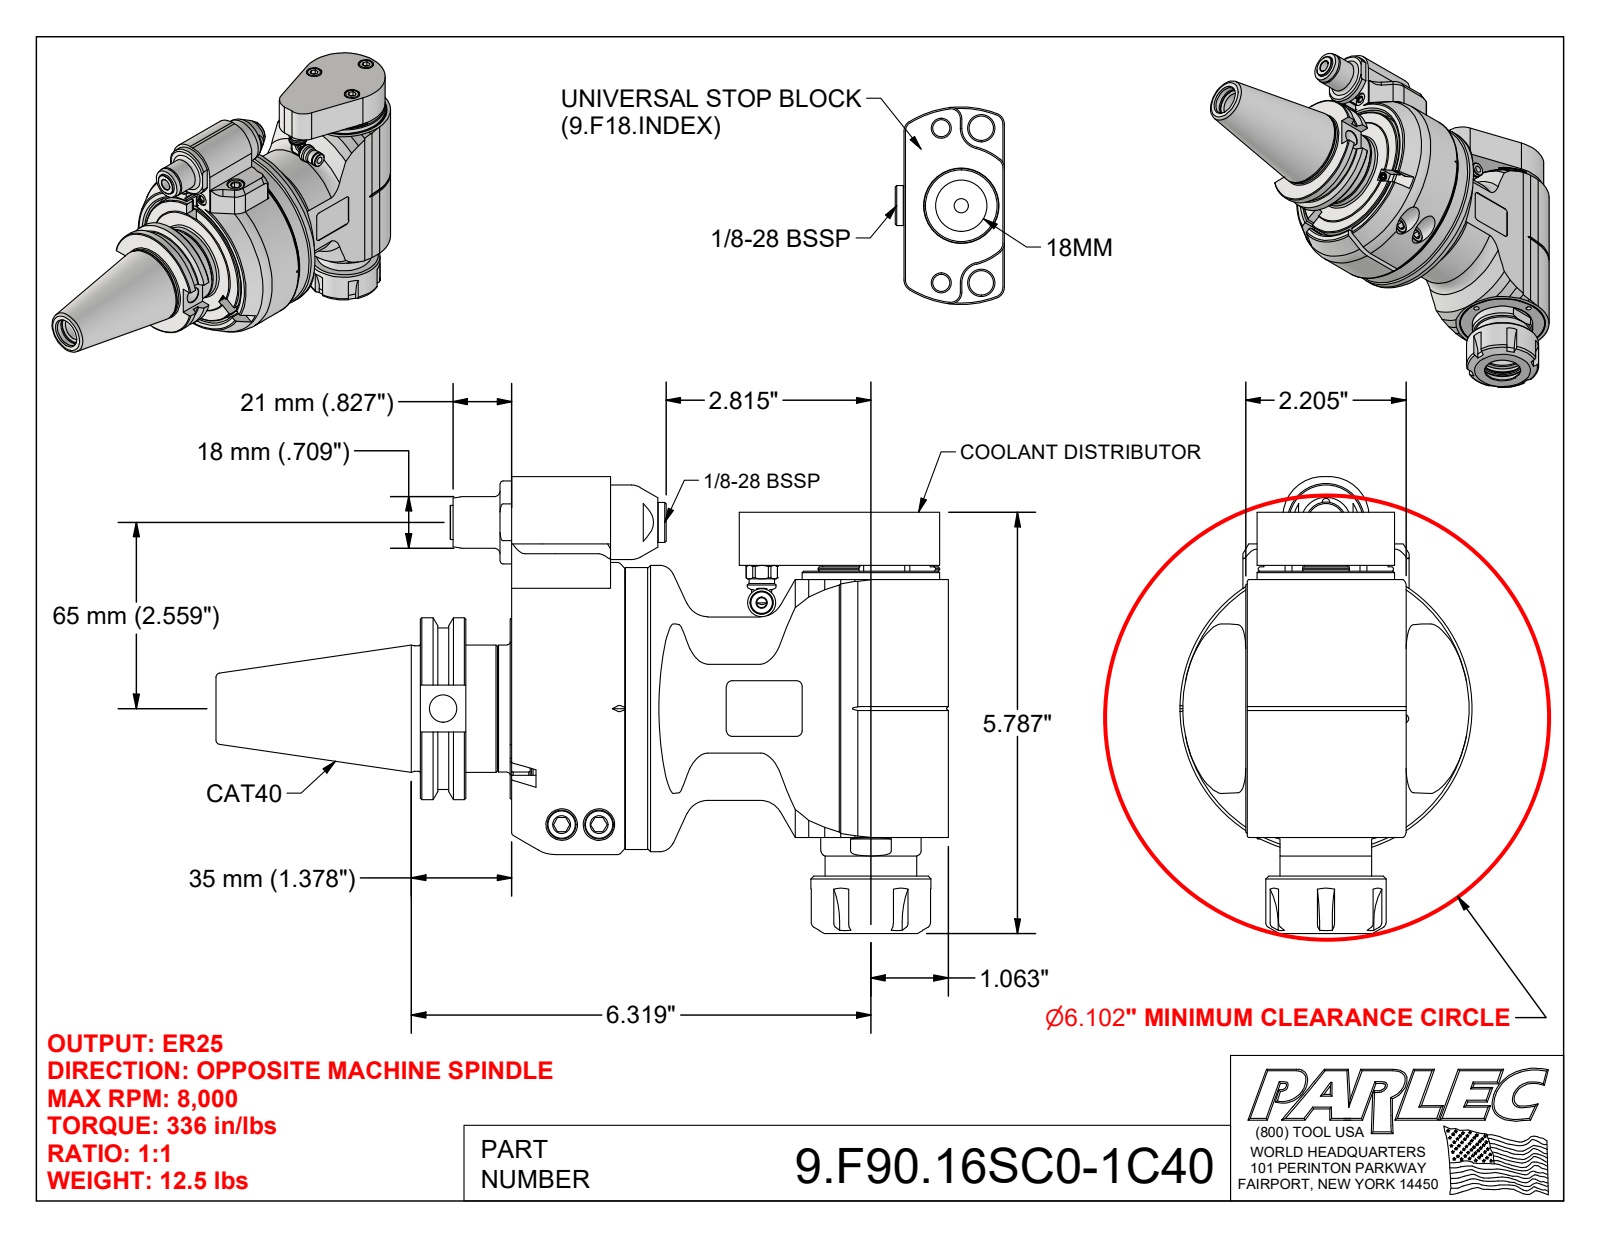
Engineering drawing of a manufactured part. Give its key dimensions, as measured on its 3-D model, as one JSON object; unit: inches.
{"part_name": "9.F90.16SC0-1C40; 9_F90_16SC0; 9_GA1_446_2 (EVO, Type 1, C40, 65mm, 35mm)", "step_written_by": "Autodesk Inventor 2022 (AUTOMOTIVE_DESIGN)", "units": "inches", "bodies": {"solids": 6, "faces": 887, "planar": 379, "cylindrical": 237, "other": 271}, "overall_size": [10.069, 6.28, 4.016], "volume_in3": 62.83, "surface_area_in2": 259.4, "round_holes": [[0.335, 21], [0.126, 8], [0.197, 3], [0.256, 3], [0.354, 3], [0.102, 2], [0.13, 2], [0.138, 2], [0.165, 2], [0.315, 2], [0.409, 2], [0.433, 2]], "round_bosses_or_shafts": [[0.394, 5], [0.335, 3], [0.709, 2], [0.472, 2], [0.315, 2], [0.236, 2], [0.098, 2], [4.016, 1]], "partial_cylinders_radius": [[0.039, 18], [0.079, 13], [0.118, 6], [0.984, 6], [0.02, 4], [0.157, 4], [0.006, 3], [0.016, 2]], "face_to_face_distances": [0.02, 0.039, 0.295, 0.276, 1.26, 0.335, 0.079, 0.315, 1.555, 2.205], "hole_center_spacings": [1.516, 2.144, 1.824, 3.002, 0.835, 2.651, 2.914, 3.031]}
